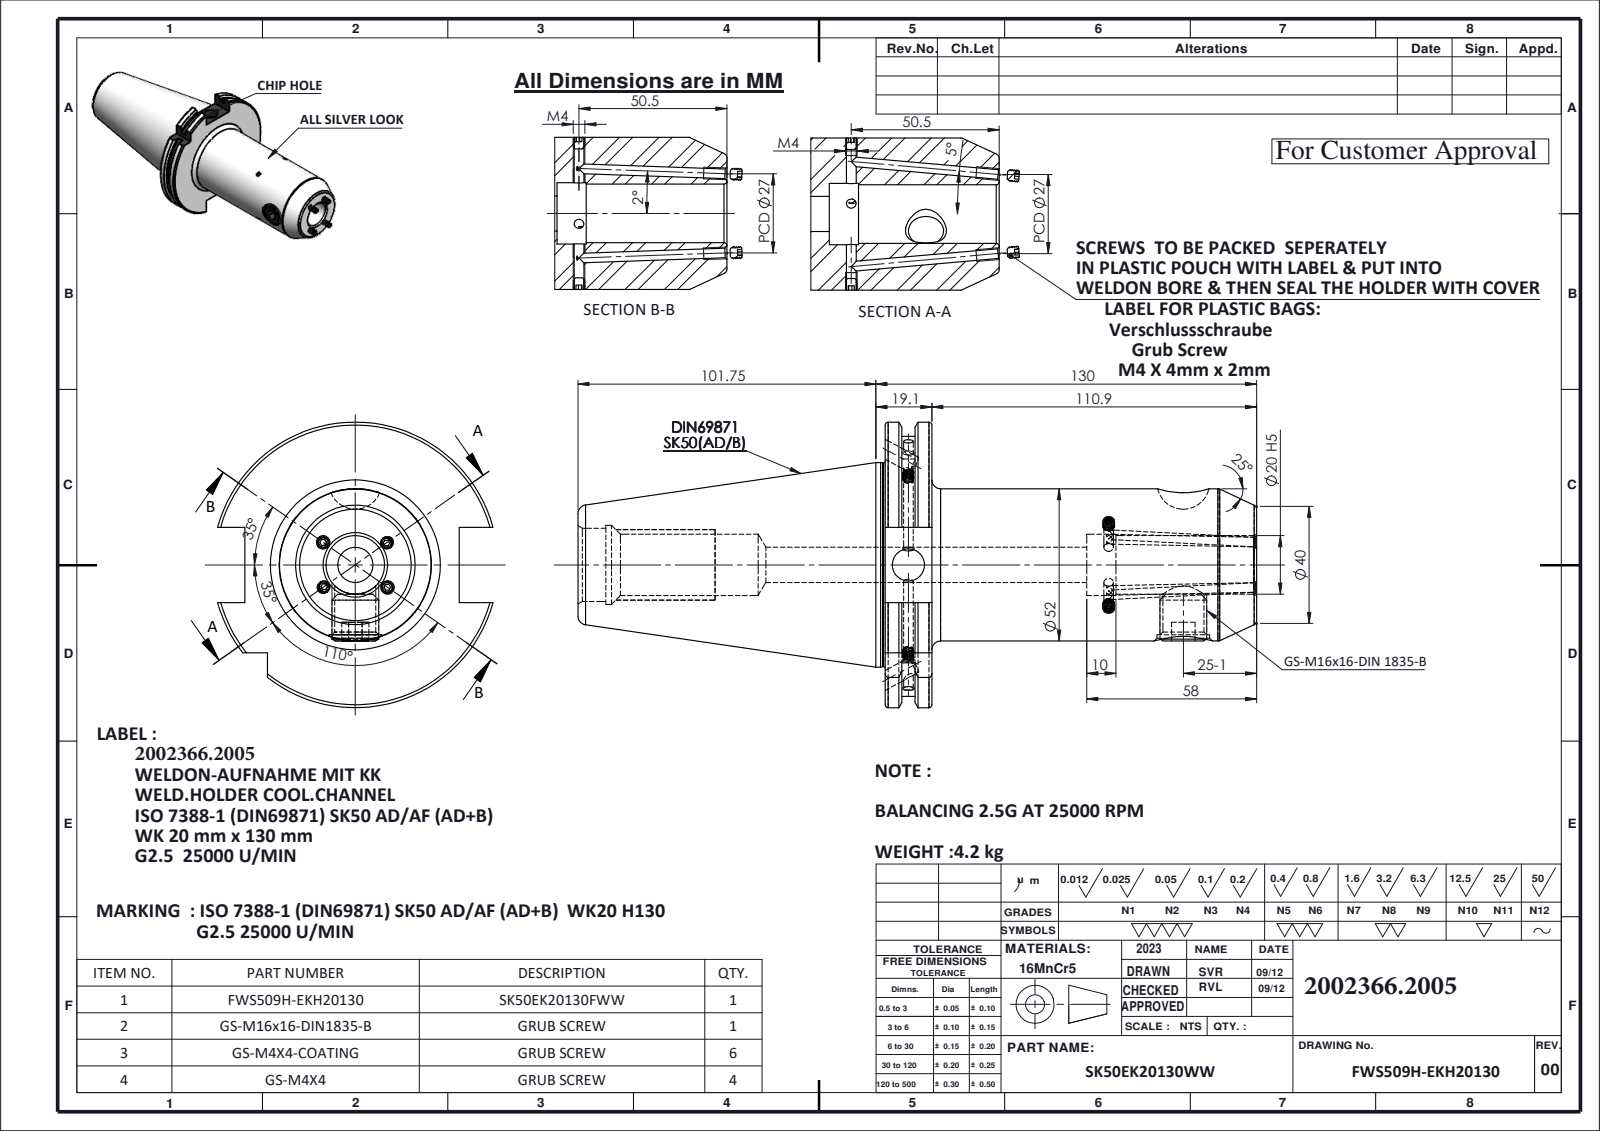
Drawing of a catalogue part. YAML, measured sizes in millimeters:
part_name: "GS-M16X16-DIN1835-B_ISO 4026 - M16 x 10-N; GS-M4X4_DIN 913 - M4 x 4-N; SK50EK20130FWW; GS-M4X4-COATING_DIN 913 - M4 x 4-N (+1 more)"
step_written_by: "SolidWorks 2023 (CONFIG_CONTROL_DESIGN)"
units: millimeters
bodies: {solids: 12, faces: 649, planar: 125, cylindrical: 179, other: 345}
overall_size: [238.7, 97.5, 94.05]
volume: 533810
surface_area: 71666
round_holes:
  - {diameter: 3.3, count: 9}
  - {diameter: 6, count: 2}
  - {diameter: 11, count: 1}
  - {diameter: 12, count: 1}
  - {diameter: 14, count: 1}
  - {diameter: 18, count: 1}
  - {diameter: 20, count: 1}
  - {diameter: 21, count: 1}
  - {diameter: 25, count: 1}
  - {diameter: 27, count: 1}
round_bosses_or_shafts:
  - {diameter: 4, count: 10}
  - {diameter: 69.85, count: 1}
  - {diameter: 69.45, count: 1}
  - {diameter: 52, count: 1}
  - {diameter: 16, count: 1}
partial_cylinders:
  - {radius: 44.9, count: 1}
  - {radius: 48.75, count: 1}
face_to_face_distances: [15.9, 126.8, 110.9, 5.65, 10.25, 121.15, 10.14, 4.49, 5.76, 116.66]
